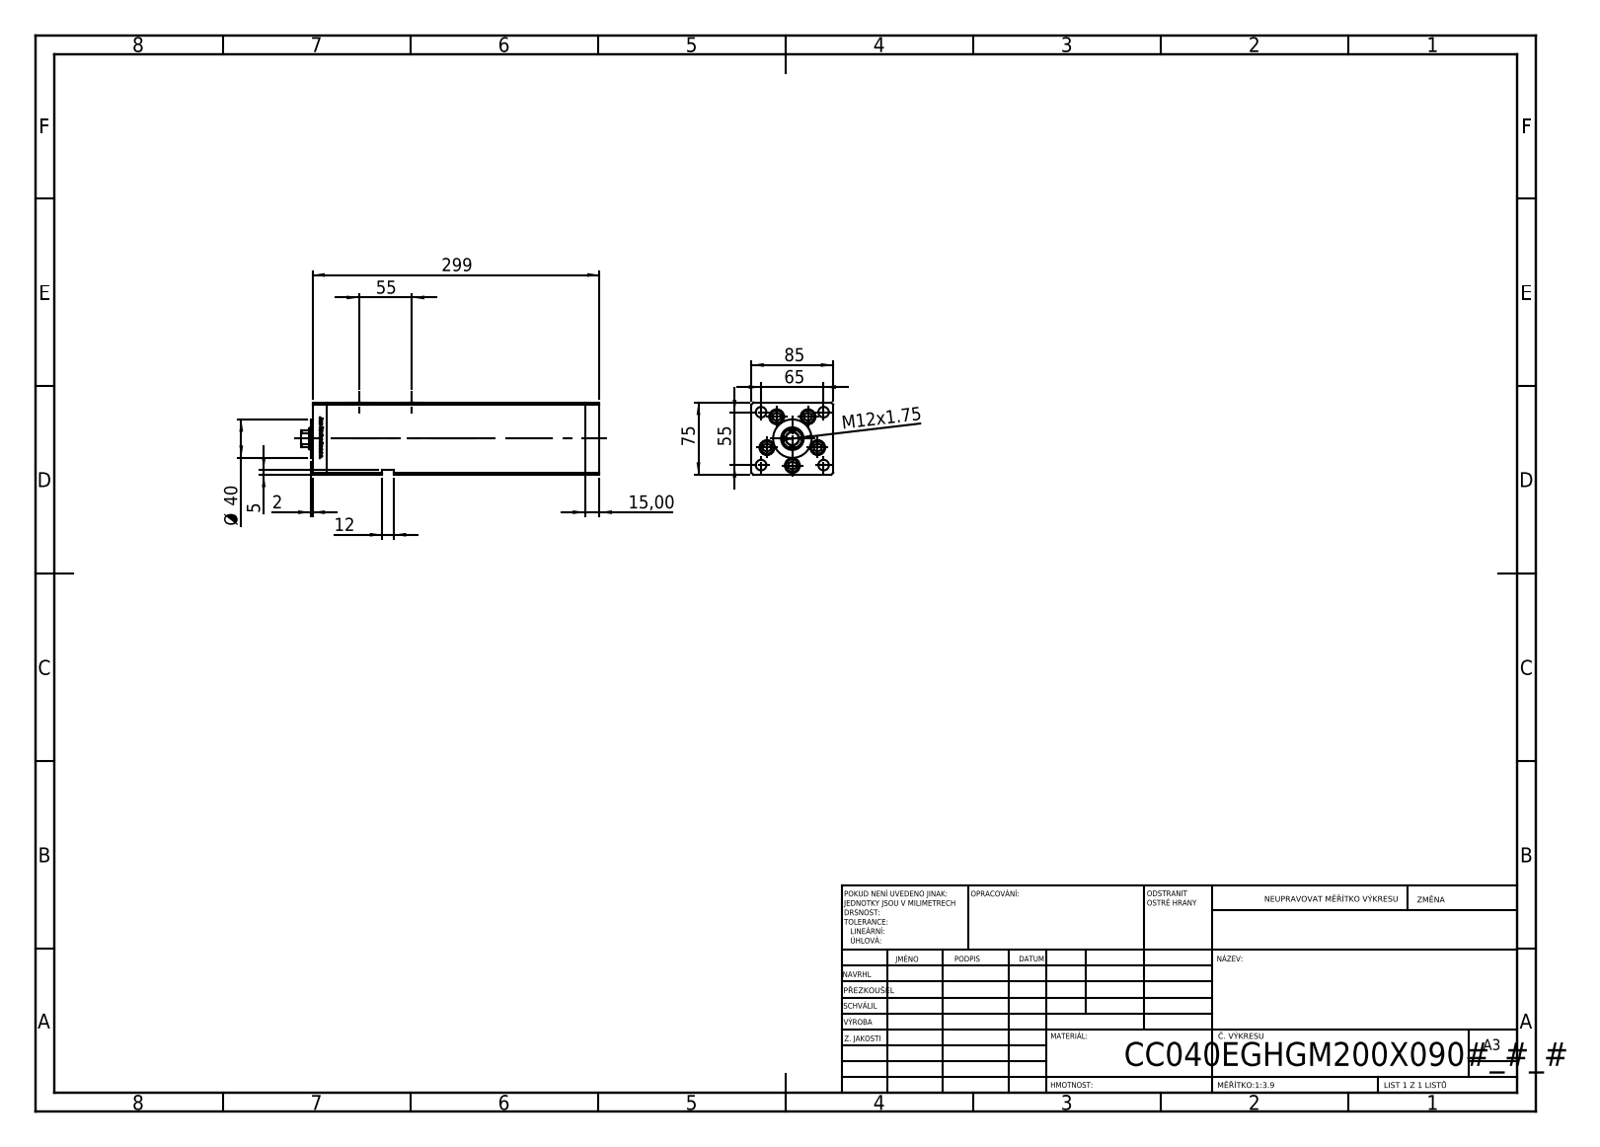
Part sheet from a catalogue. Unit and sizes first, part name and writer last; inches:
Units: inches
Overall size (bounding box): 12.205 × 3.346 × 2.953
Round holes (diameter × count): ⌀0.433 ×9, ⌀0.61 ×5, ⌀0.413 ×4, ⌀0.65 ×4, ⌀0.079 ×2, ⌀0.518 ×2, ⌀0.531 ×1, ⌀0.866 ×1, ⌀0.925 ×1
Round bosses / shafts (diameter × count): ⌀0.571 ×5, ⌀0.315 ×5, ⌀1.575 ×1
Partial cylindrical surfaces — rounded edges, fillets, slot ends (radius × count): R0.037 ×2, R0.413 ×1
Main face-to-face distances: 3.346, 2.953, 0.591, 10.571, 11.161, 0.413, 11.752, 2.539, 2.697, 1.23
Hole centre spacings: 1.102, 1.676, 2.165, 2.559, 3.352, 0.664, 0.755, 1.273
Volume: 98 in³ · Surface area: 366.2 in²
Bodies: 14 solids, 1212 faces (473 planar, 165 cylindrical, 574 other)
Part name (STEP PRODUCT): V220C_E MIDDLE; ALLEN BOLT; V220C_VC_E; V220C_FRONT_E (+1 more)
STEP written by: SolidWorks 2019 (CONFIG_CONTROL_DESIGN)
